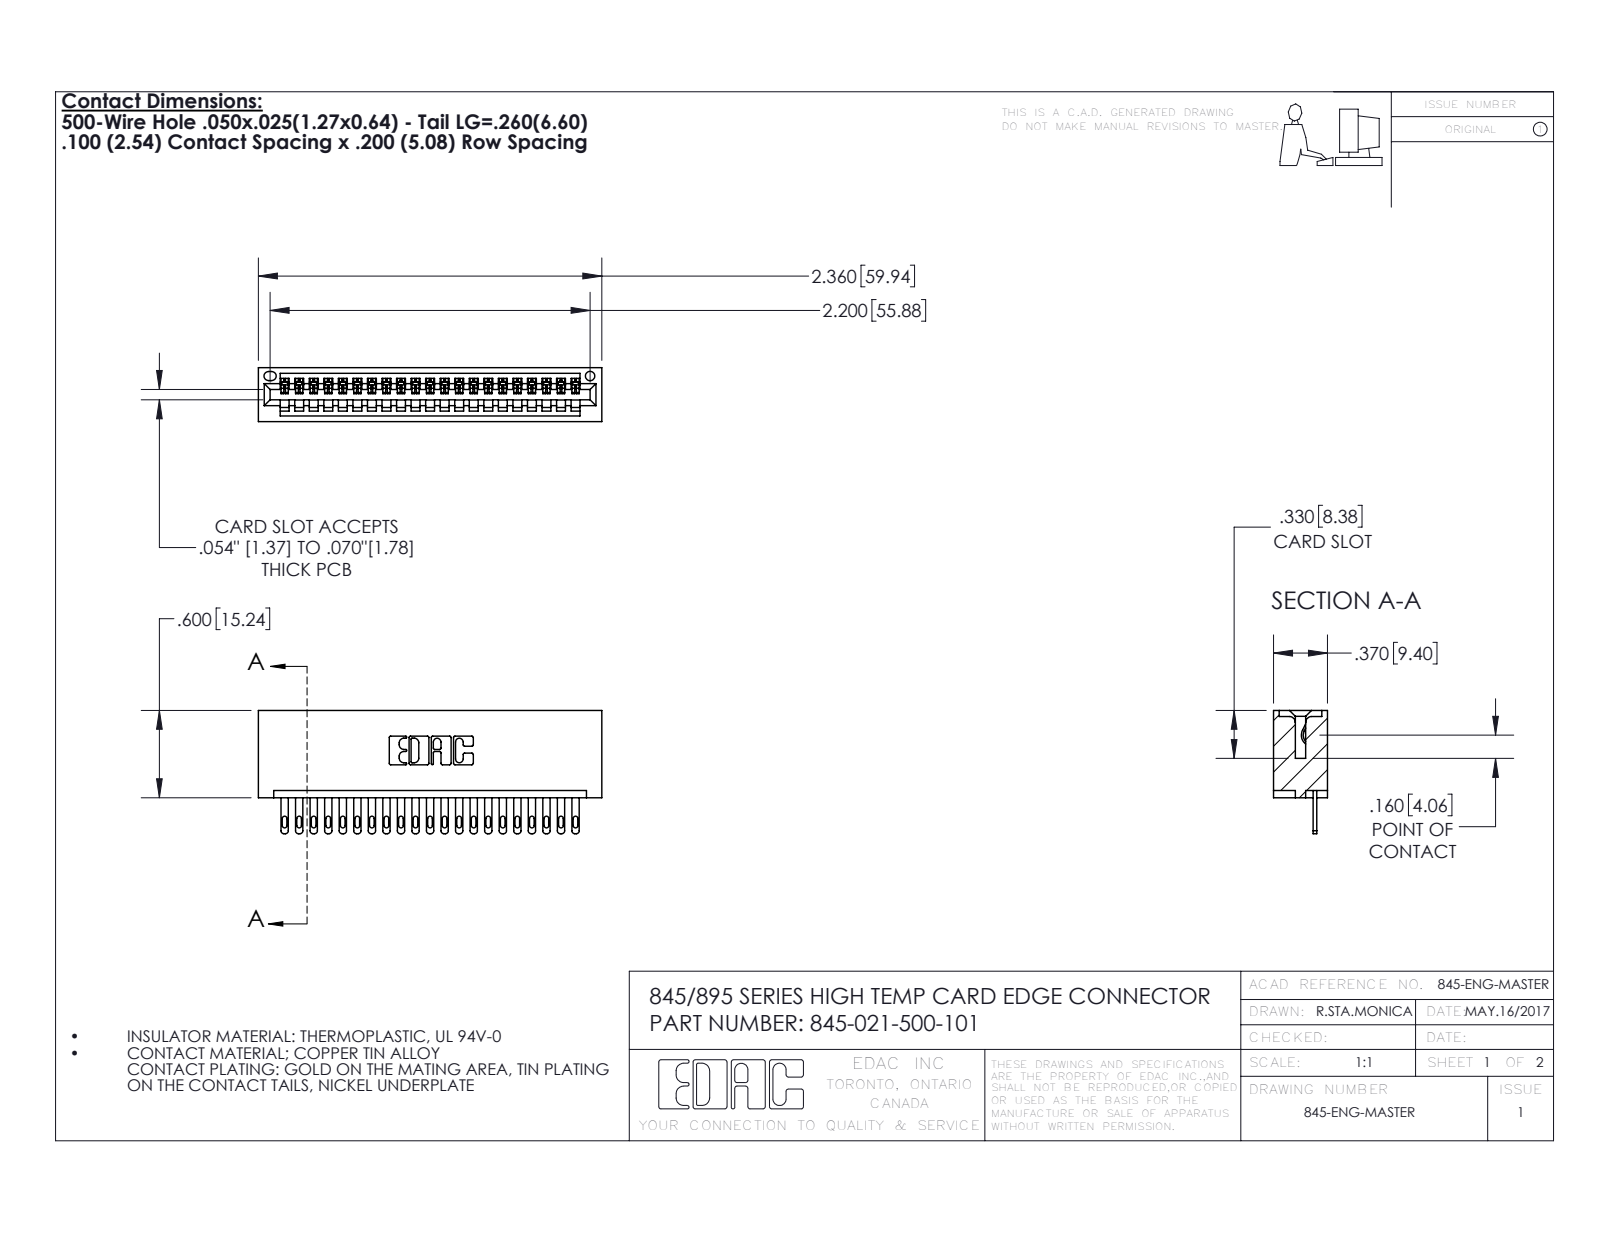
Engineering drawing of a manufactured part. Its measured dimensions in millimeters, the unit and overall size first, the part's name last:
Units: millimetres
Overall size (bounding box): 59.9 × 21.5 × 9.4
Round holes (diameter × count): ⌀1.6 ×1
Partial cylindrical surfaces — rounded edges, fillets, slot ends (radius × count): R0.2 ×42, R0.4 ×42, R0.5 ×42, R0.3 ×22, R0.2 ×6, R0.8 ×6, R0.7 ×3, R0.8 ×2
Main face-to-face distances: 7.6, 1.8, 5.1, 9.4, 2.5, 6.9, 0.6, 5.7, 2.5, 3.8
Volume: 6 110 mm³ · Surface area: 8 084 mm²
Bodies: 22 solids, 1252 faces (790 planar, 462 cylindrical, 0 other)
Part name (STEP PRODUCT): 345-292-001_345-293-100; 345-021-500-101; 345 Part_No Mounting Lugs
STEP written by: SolidWorks 2016 (CONFIG_CONTROL_DESIGN)
